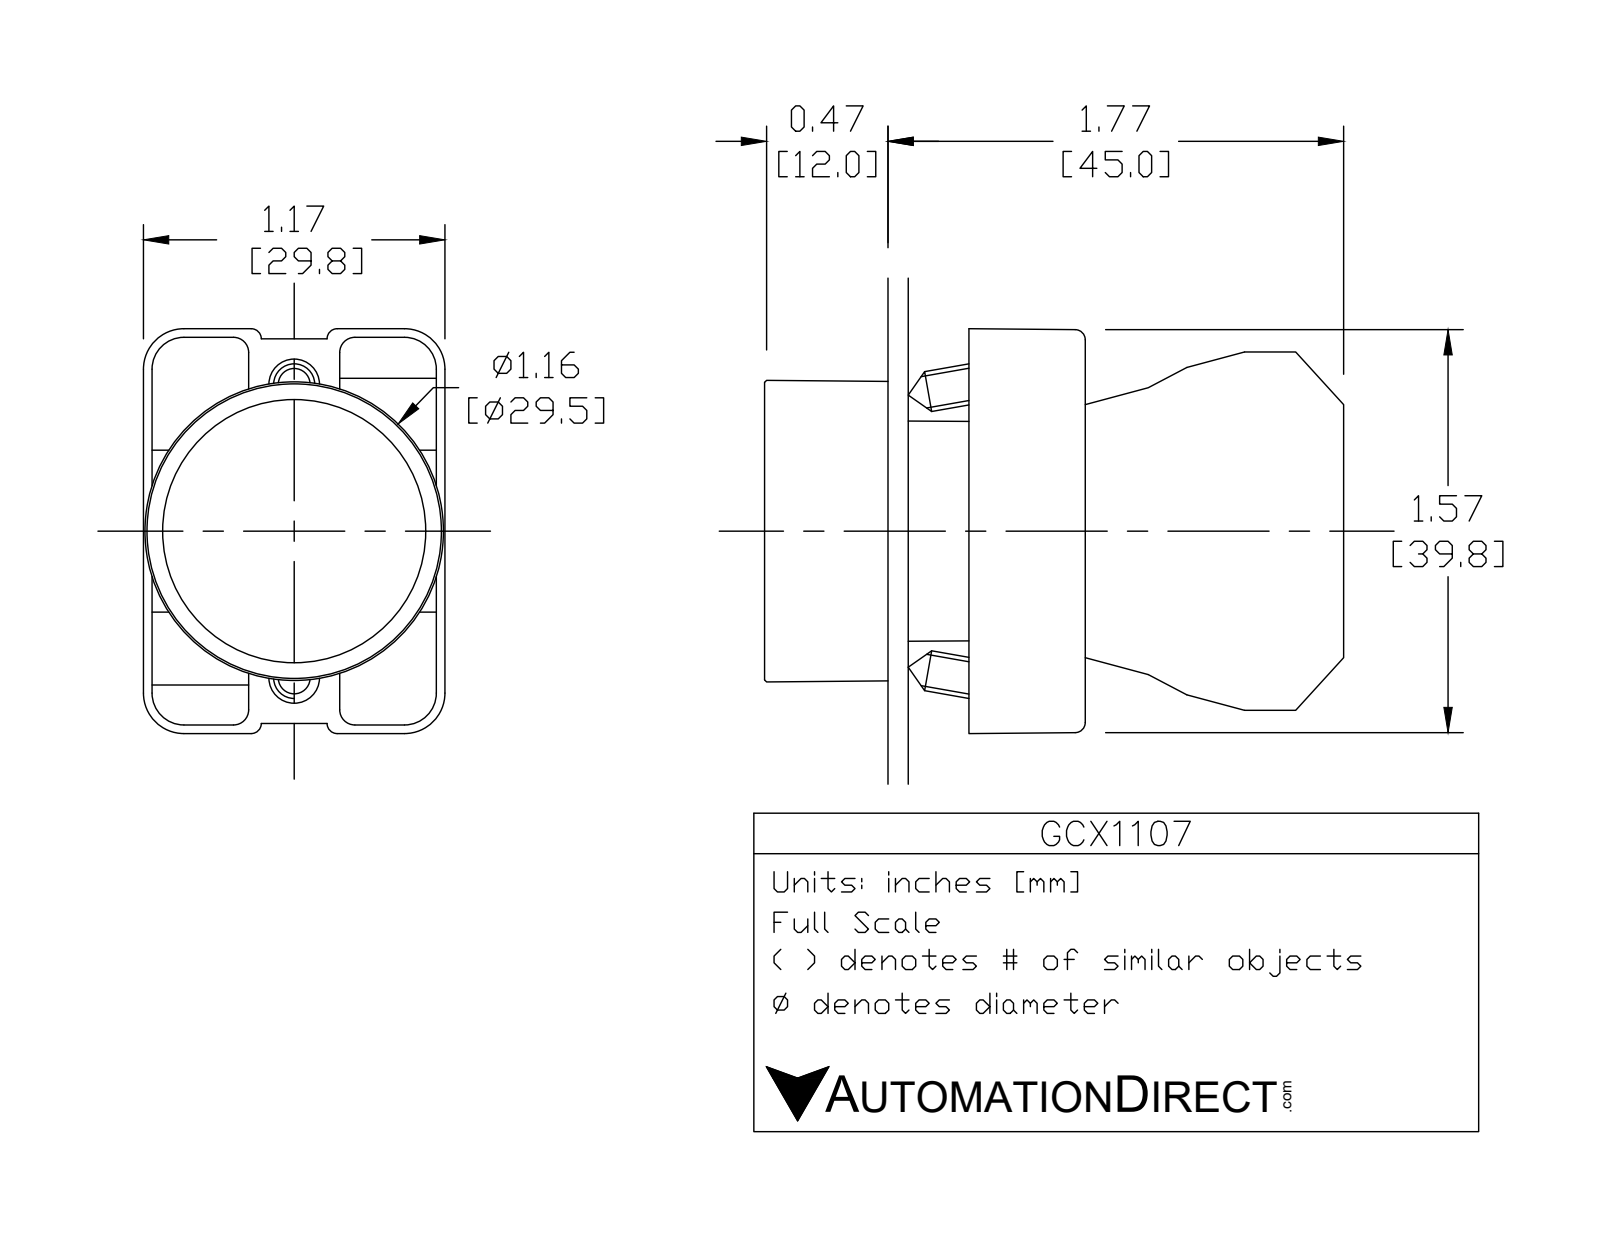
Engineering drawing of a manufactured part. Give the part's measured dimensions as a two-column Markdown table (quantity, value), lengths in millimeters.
| quantity | value |
| --- | --- |
| part name | ecx1029; GCX1107; GCX1107 OPERATOR; ecx1040 |
| STEP written by | SolidWorks 2016 (AUTOMOTIVE_DESIGN) |
| units | millimeters |
| bodies | 6 solids, 386 faces (227 planar, 132 cylindrical, 27 other) |
| overall size | 56.3 × 40.2 × 29.9 |
| volume | 28 530 mm³ |
| surface area | 17 510 mm² |
| round holes (diameter × count) | 2 × 2, 3.1 × 2, 3.3 × 2, 2.2 × 1, 5 × 1, 22.3 × 1, 22.6 × 1, 26 × 1 |
| round bosses / shafts (diameter × count) | 4 × 2, 29.8 × 1, 25.5 × 1, 24 × 1, 21.7 × 1, 19.8 × 1 |
| partial cylindrical surfaces (radius × count) | 1.5 × 24, 1 × 12, 3.1 × 12, 4 × 12, 1 × 4, 3.3 × 2, 0.5 × 1, 1.6 × 1 |
| main face-to-face distances | 18.3, 14.7, 0.8, 12, 30.3, 0.8, 17.5, 15.2, 29.5, 27.2 |
| hole center spacings | 6, 13.8, 12, 12.4 |
